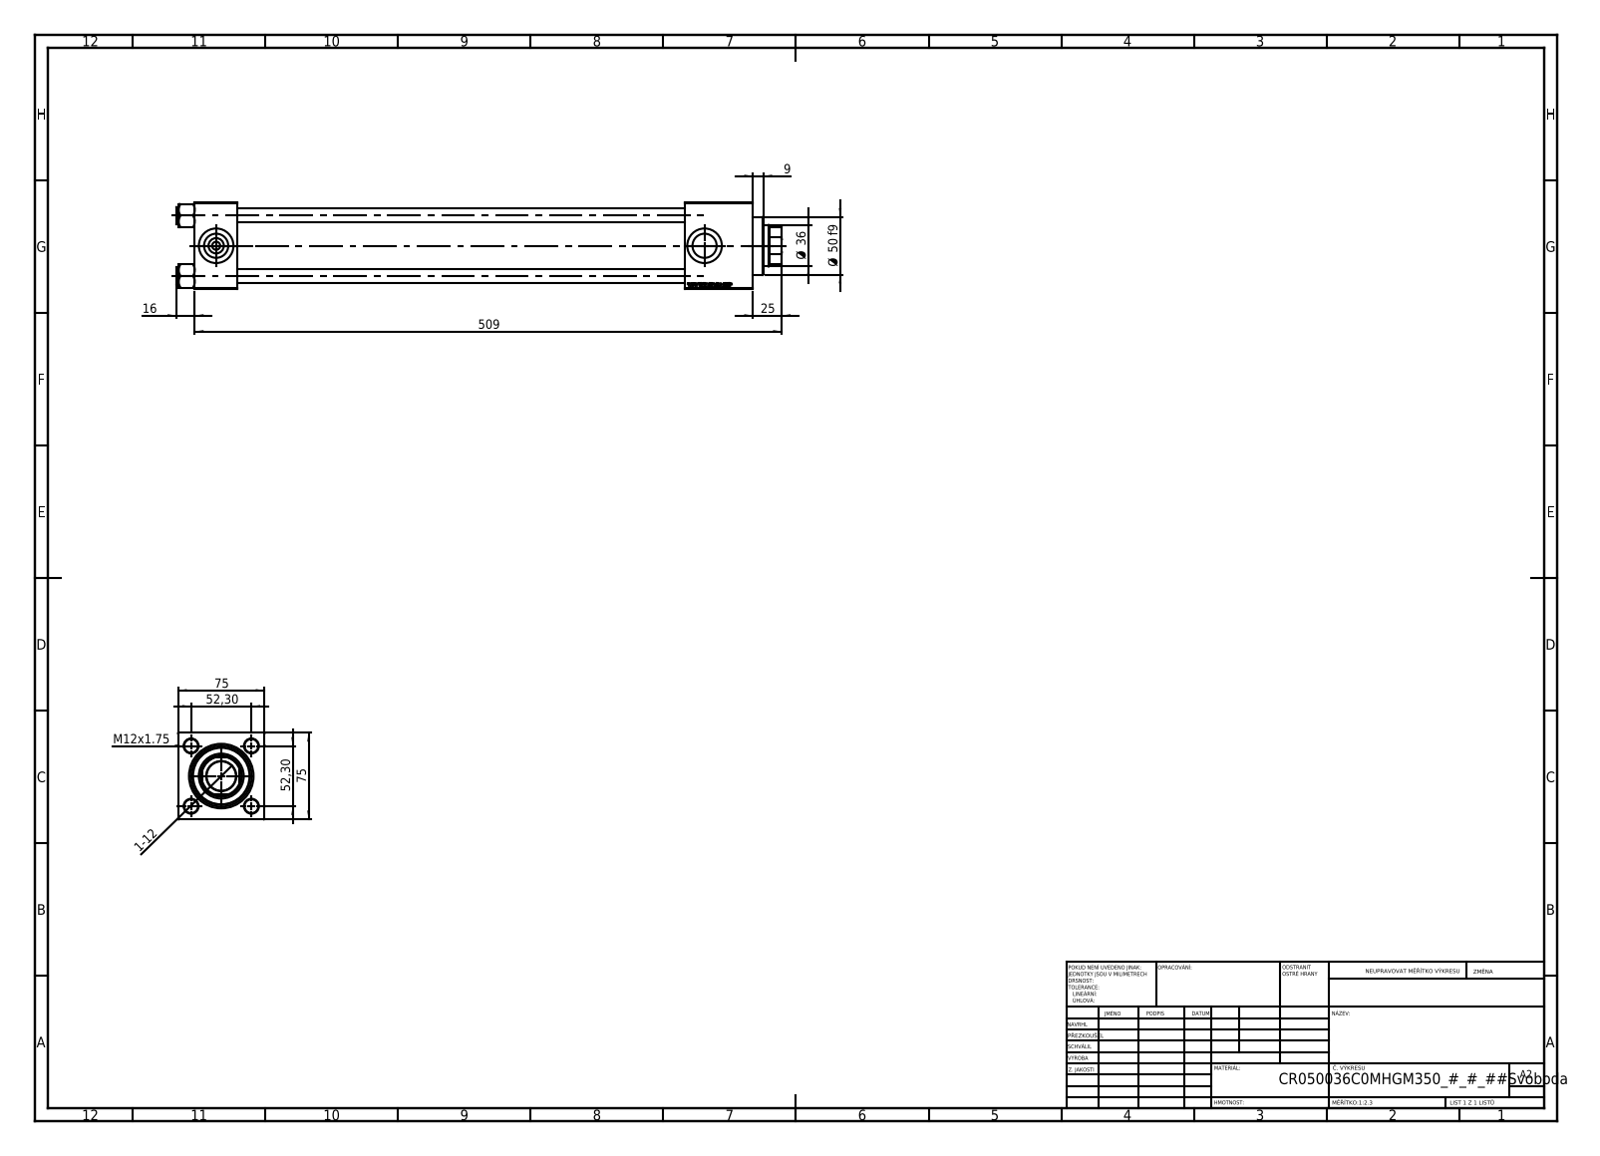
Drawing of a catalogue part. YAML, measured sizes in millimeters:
part_name: "V215CR_C_Body; V215_VC_A; NUT_M5_C; V215CR_VCP_C (+1 more)"
step_written_by: "SolidWorks 2019 (CONFIG_CONTROL_DESIGN)"
units: millimeters
bodies: {solids: 11, faces: 1148, planar: 526, cylindrical: 86, other: 536}
overall_size: [525, 75.54, 75]
volume: 1336000
surface_area: 352468
round_holes:
  - {diameter: 12, count: 4}
  - {diameter: 7, count: 2}
  - {diameter: 20.96, count: 2}
  - {diameter: 30, count: 2}
  - {diameter: 25.5, count: 1}
  - {diameter: 36, count: 1}
  - {diameter: 39, count: 1}
  - {diameter: 41, count: 1}
  - {diameter: 53, count: 1}
round_bosses_or_shafts:
  - {diameter: 15, count: 4}
  - {diameter: 56, count: 1}
  - {diameter: 50, count: 1}
partial_cylinders:
  - {radius: 17.5, count: 1}
face_to_face_distances: [75, 37, 425, 388, 484, 447, 59, 455.3, 418.3, 30.3]
hole_center_spacings: [36.98, 52.3, 73.96, 423.5]
